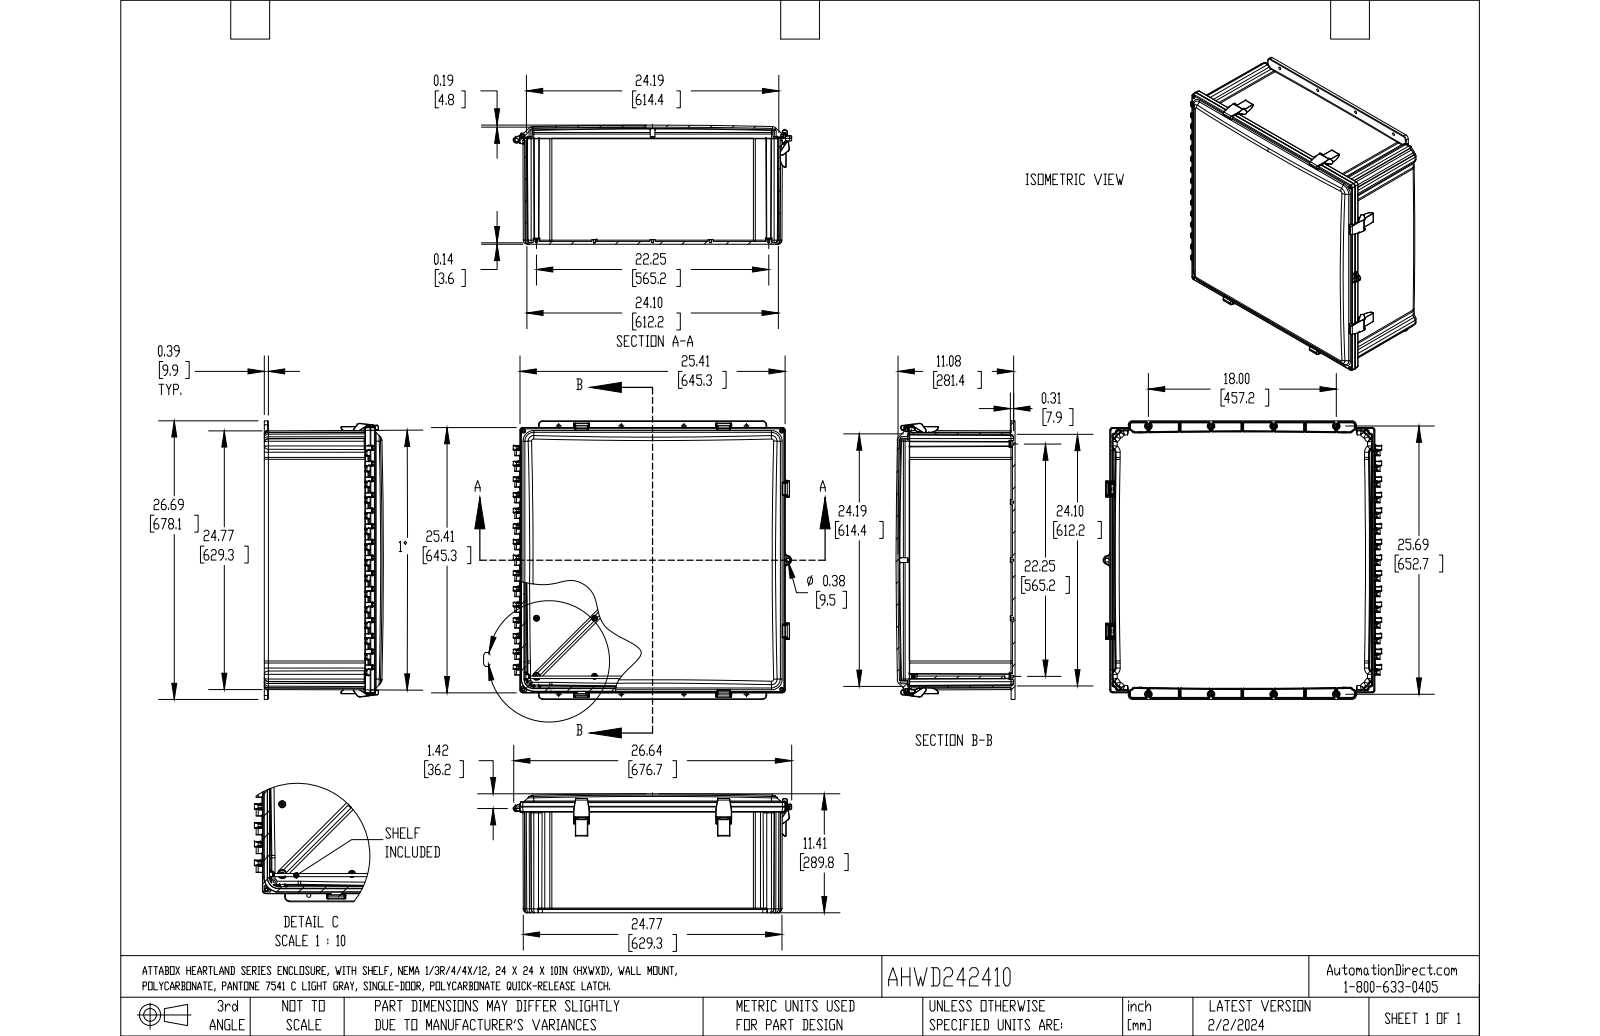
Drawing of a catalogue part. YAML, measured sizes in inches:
part_name: "AHWD242410_WESLEY1"
step_written_by: "SolidWorks 2023 (AUTOMOTIVE_DESIGN)"
units: inches
bodies: {solids: 20, faces: 1770, planar: 742, cylindrical: 748, other: 280}
overall_size: [26.695, 26.676, 11.408]
volume: 437.2
surface_area: 5664
round_holes:
  - {diameter: 0.187, count: 21}
  - {diameter: 0.316, count: 8}
  - {diameter: 0.186, count: 7}
  - {diameter: 0.195, count: 4}
  - {diameter: 0.246, count: 4}
  - {diameter: 0.26, count: 4}
  - {diameter: 0.39, count: 4}
  - {diameter: 0.19, count: 2}
  - {diameter: 0.267, count: 1}
  - {diameter: 0.327, count: 1}
  - {diameter: 0.375, count: 1}
round_bosses_or_shafts:
  - {diameter: 0.487, count: 20}
  - {diameter: 0.2, count: 6}
  - {diameter: 0.625, count: 4}
  - {diameter: 0.438, count: 4}
  - {diameter: 0.373, count: 2}
  - {diameter: 0.492, count: 1}
  - {diameter: 0.313, count: 1}
  - {diameter: 0.19, count: 1}
partial_cylinders:
  - {radius: 0.035, count: 123}
  - {radius: 0.025, count: 32}
  - {radius: 0.063, count: 16}
  - {radius: 0.065, count: 12}
  - {radius: 0.25, count: 8}
  - {radius: 0.355, count: 8}
  - {radius: 0.909, count: 8}
  - {radius: 0.3, count: 7}
face_to_face_distances: [0.14, 0.25, 24.195, 23.444, 23.194, 0.751, 1.001, 24.195, 0.5, 10.14]
hole_center_spacings: [11.75, 24.75, 12.391, 12.391, 16.617, 24.133, 24.133, 26.274]
